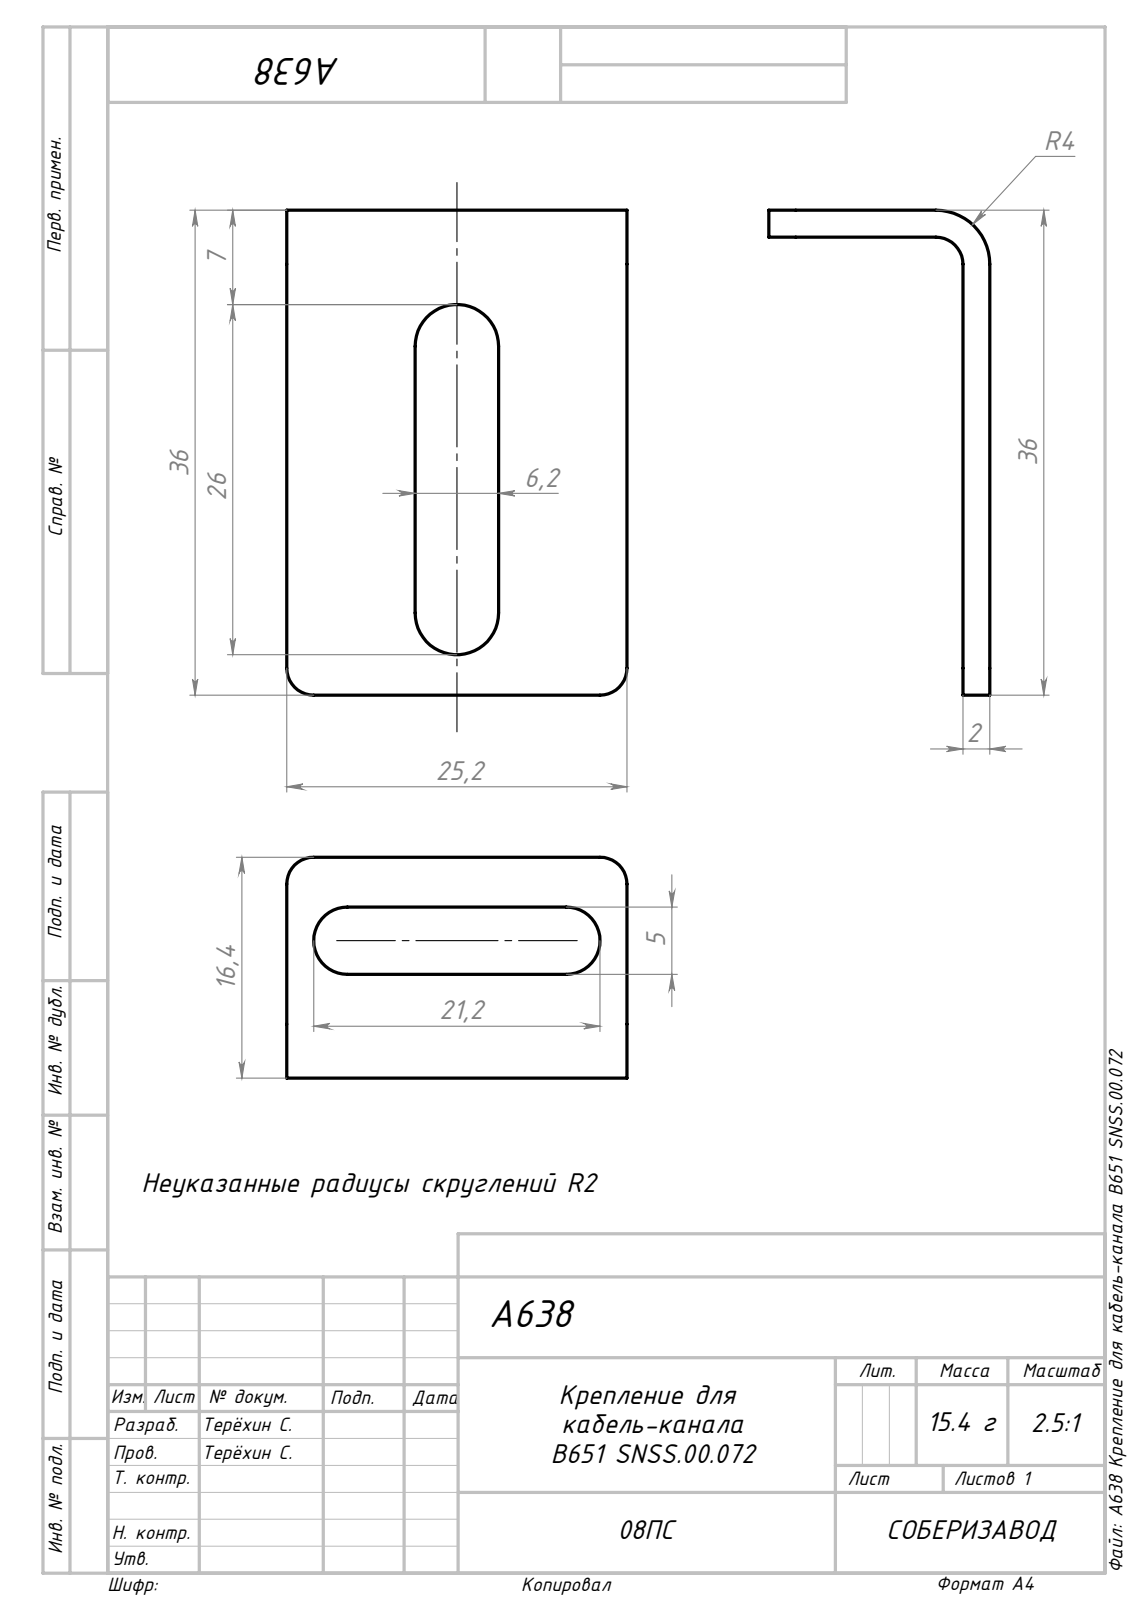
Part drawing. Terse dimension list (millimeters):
name: A638 Крепление для кабель-канала B651 SNSS.00.072_1; Сборка1
written by: SolidWorks 2022 (AUTOMOTIVE_DESIGN)
unit: mm
bodies: 1 solid, 27 faces (16 planar, 11 cylindrical, 0 other)
size: 36 × 25.25 × 16.4
volume: 1 966 mm³; area: 2 471 mm²
rounds: 5× R2, 2× R2.5, 2× R3.1, 1× R4
face distances: 2, 25.25, 34, 36, 14.4, 16.4, 15.73, 9.52, 9.53, 6.2
